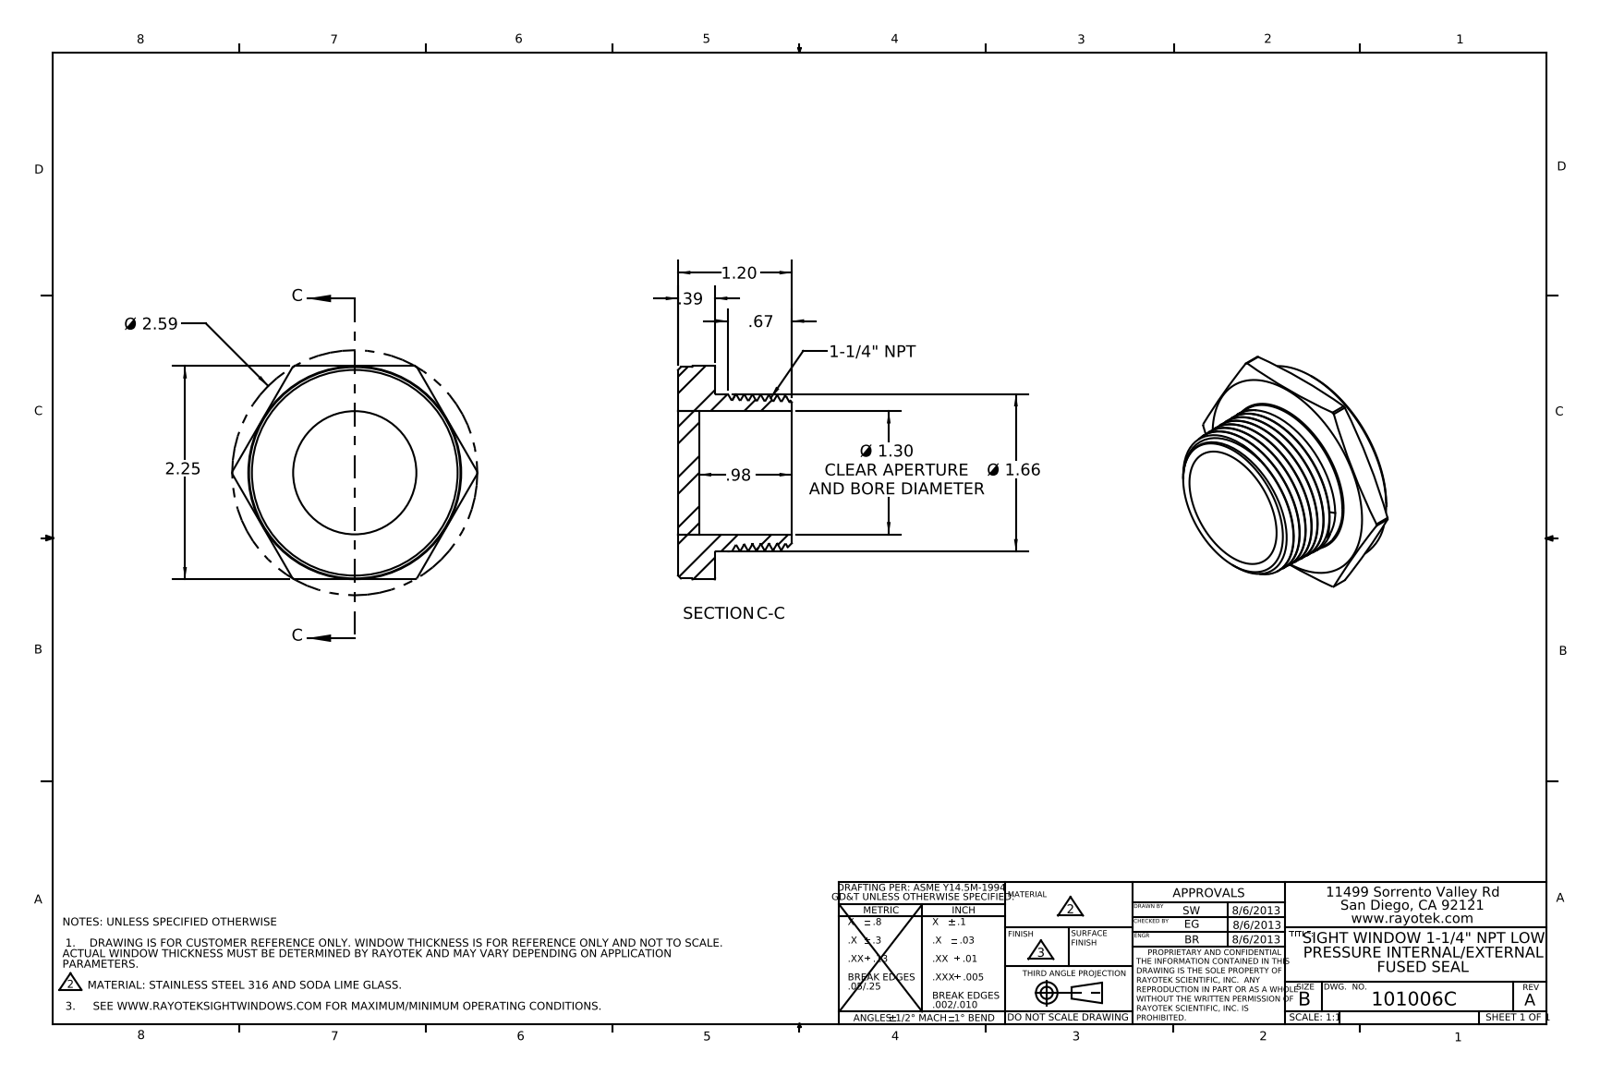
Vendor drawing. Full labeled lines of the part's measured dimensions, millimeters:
Part name (STEP PRODUCT): 403006
STEP written by: SolidWorks 2012 (AUTOMOTIVE_DESIGN)
Units: millimetres
Bodies: 2 solids, 60 faces (14 planar, 15 cylindrical, 31 other)
Overall size (bounding box): 65.7 × 57.2 × 30.5
Volume: 31 660 mm³ · Surface area: 15 210 mm²
Round holes (diameter × count): ⌀33 ×1
Round bosses / shafts (diameter × count): ⌀56.6 ×1, ⌀42.2 ×1
Partial cylindrical surfaces — rounded edges, fillets, slot ends (radius × count): R32.8 ×1
Main face-to-face distances: 9.9, 5.6, 4.3, 57.2, 30.5, 24.9, 20.6, 57.2
